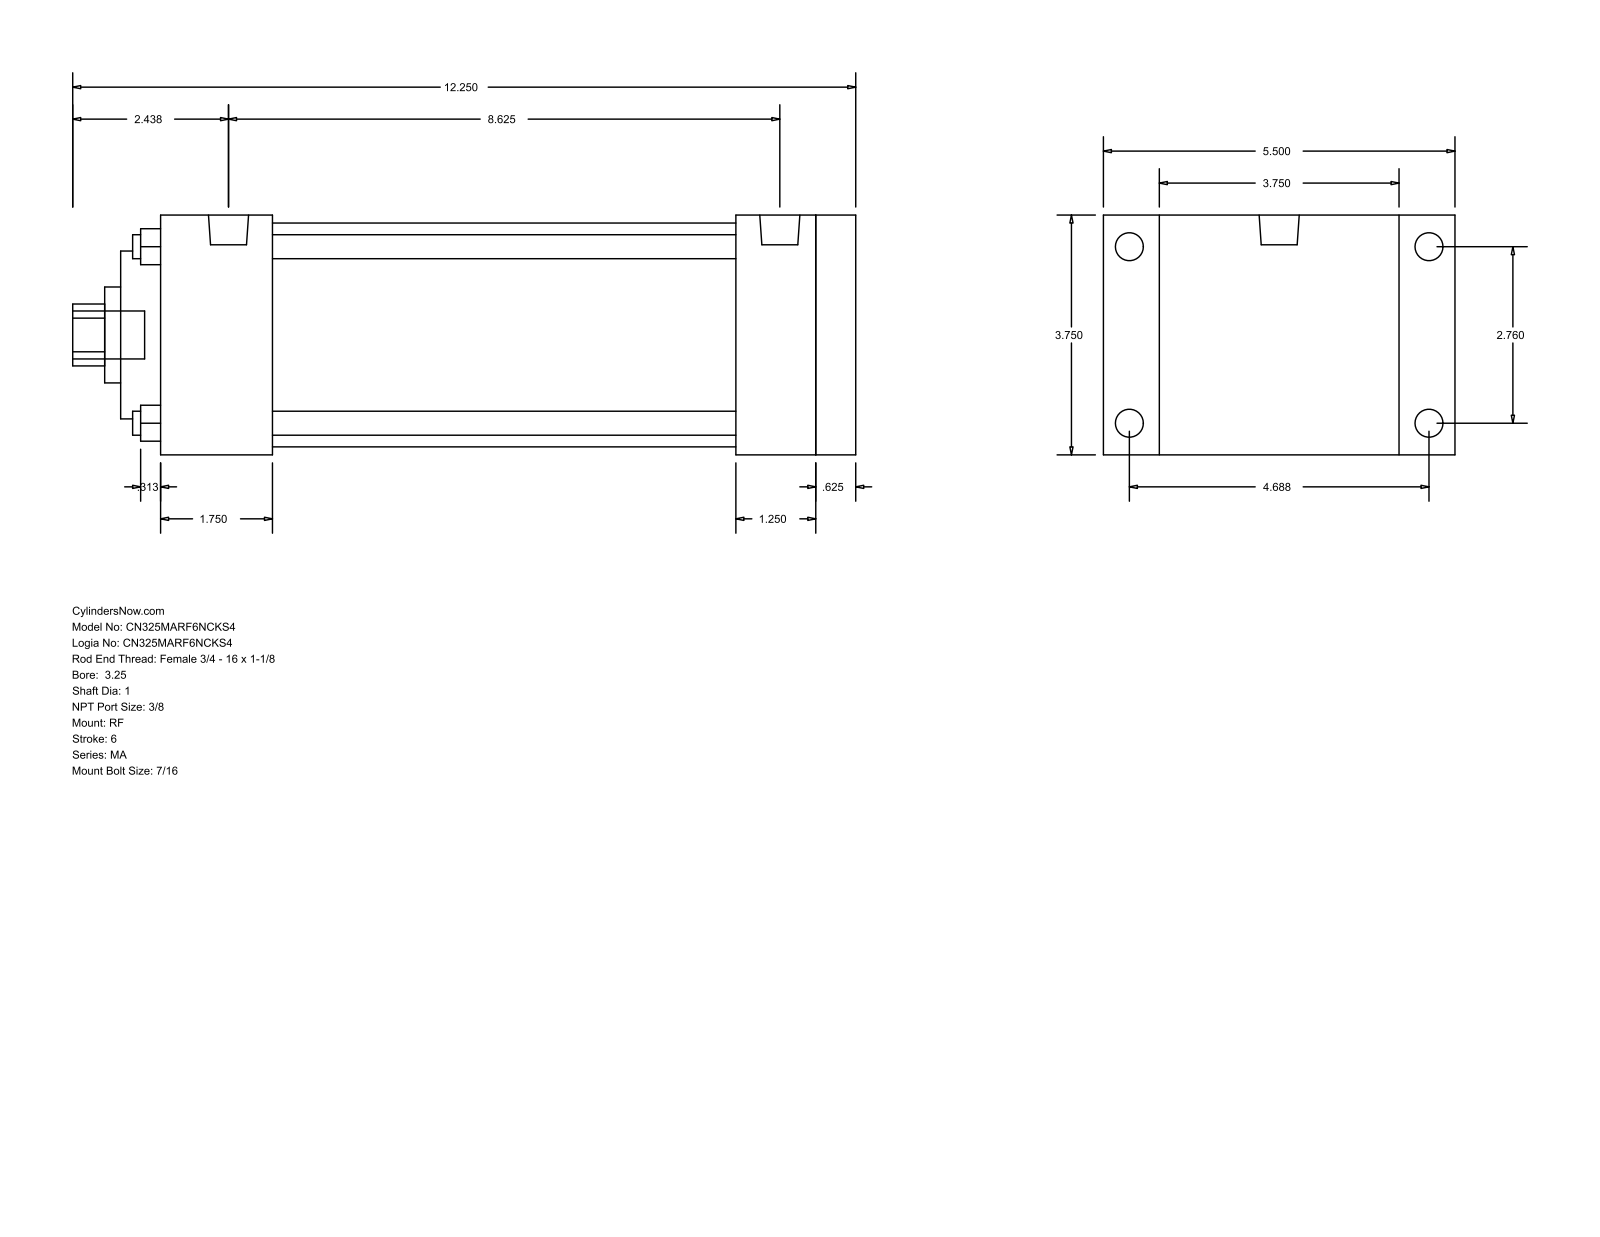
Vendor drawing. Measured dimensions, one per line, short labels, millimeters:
name: MA_RF__0325_1
written by: GSSL Pune (CONFIG_CONTROL_DESIGN)
unit: mm
bodies: 0 solids, 94 faces (65 planar, 29 cylindrical, 0 other)
size: 311.15 × 139.7 × 95.25
holes: 4× ⌀9.53, 1× ⌀25.4, 1× ⌀38.1, 1× ⌀66.67, 1× ⌀88.9
bosses: 8× ⌀11.11, 2× ⌀15.93, 1× ⌀19.05
rounds: 1× R12.29
face distances: 95.24, 276.23, 260.35, 15.88, 22.23, 117.47, 15.87, 228.6, 31.75, 47.63
hole spacings: 49.57, 70.1, 99.14
